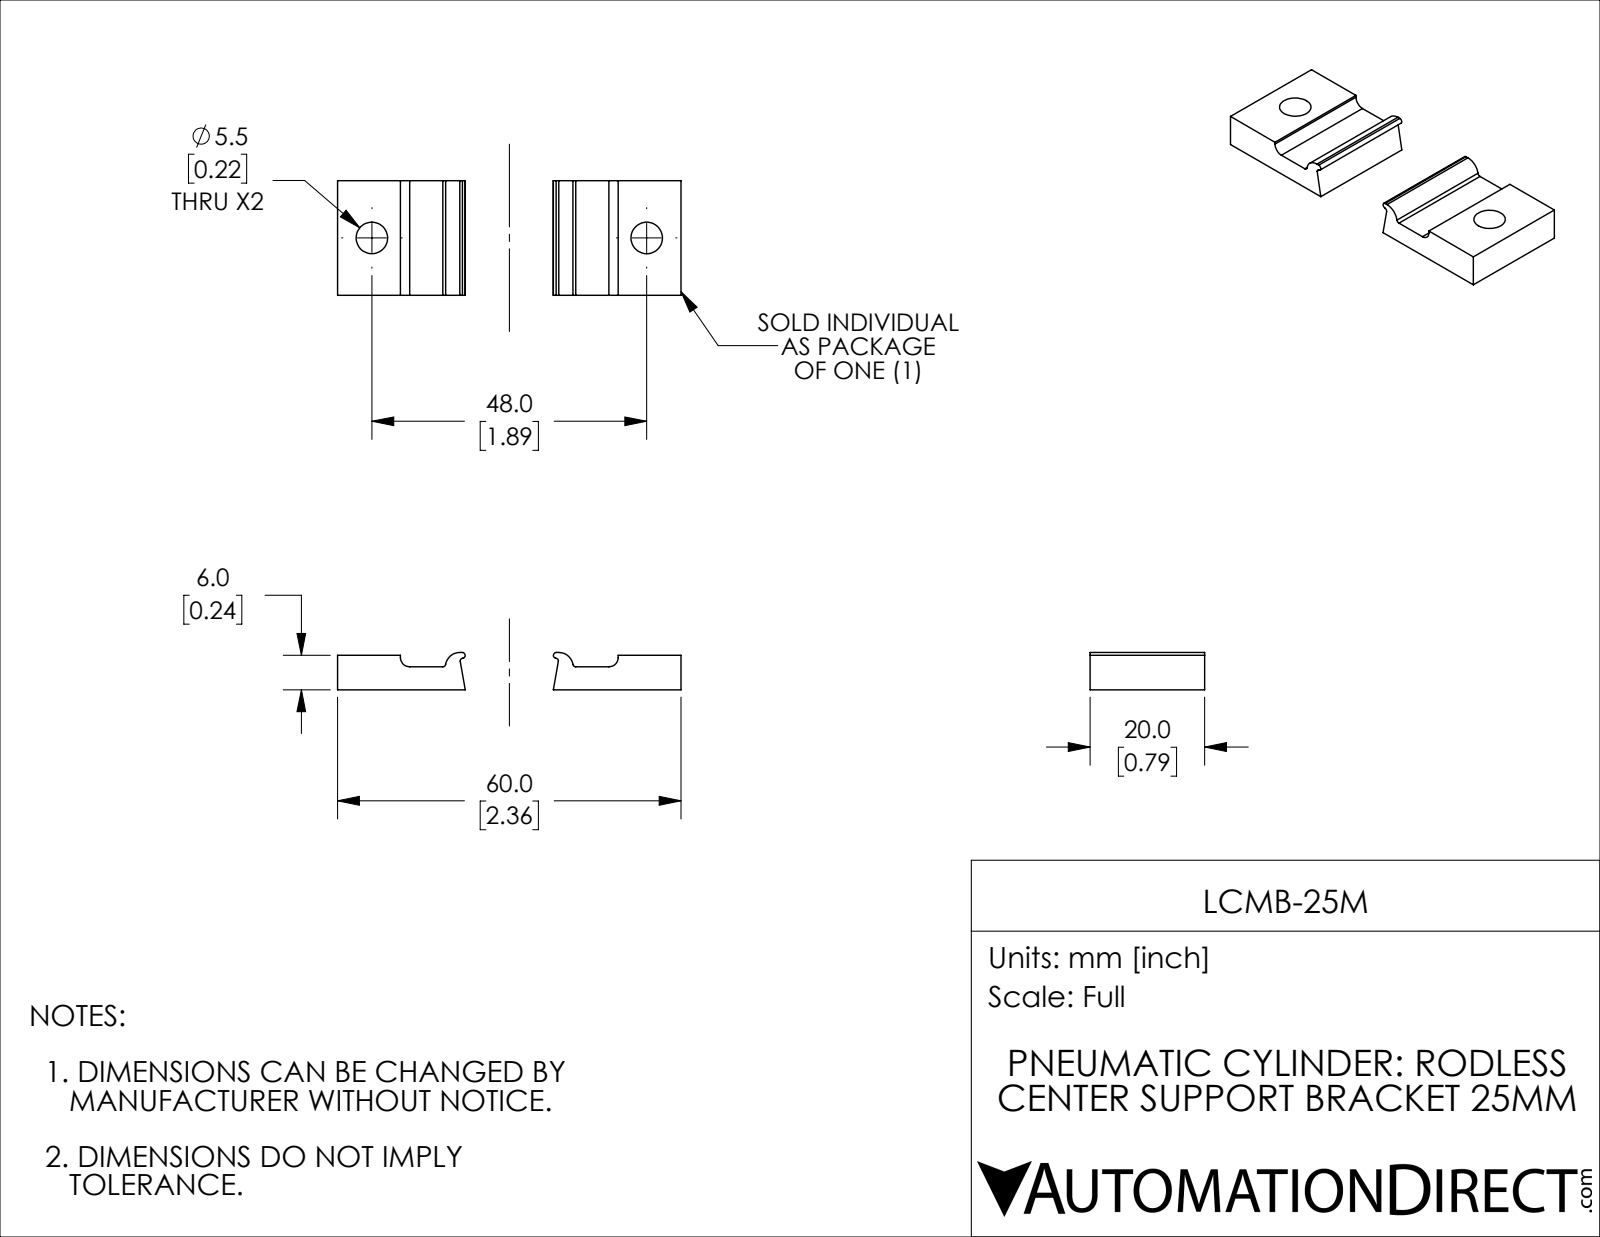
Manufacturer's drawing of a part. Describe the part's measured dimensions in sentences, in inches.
The part is named "LCMB-25M". Its 3-D file was written by "SolidWorks 2019 (CONFIG_CONTROL_DESIGN)". It is 2 solids with 34 faces: 18 planar, 16 cylindrical and 0 other. Overall it measures 2.362 by 0.787 by 0.256 inches. Its volume is 0.267 cubic inches and its surface area 4.615 square inches. Round holes: 2 of diameter 0.217. Partial cylindrical surfaces (rounded edges, fillets, slot ends): 6 of radius 0.02, 2 of radius 0.063, 2 of radius 0.098. The main face-to-face distances are 0.236, 0.787, 0.157, 0.079, 2.362, 0.256, 0.098, 0.02, 0.433, 1.929. The hole center spacings are 1.89.
